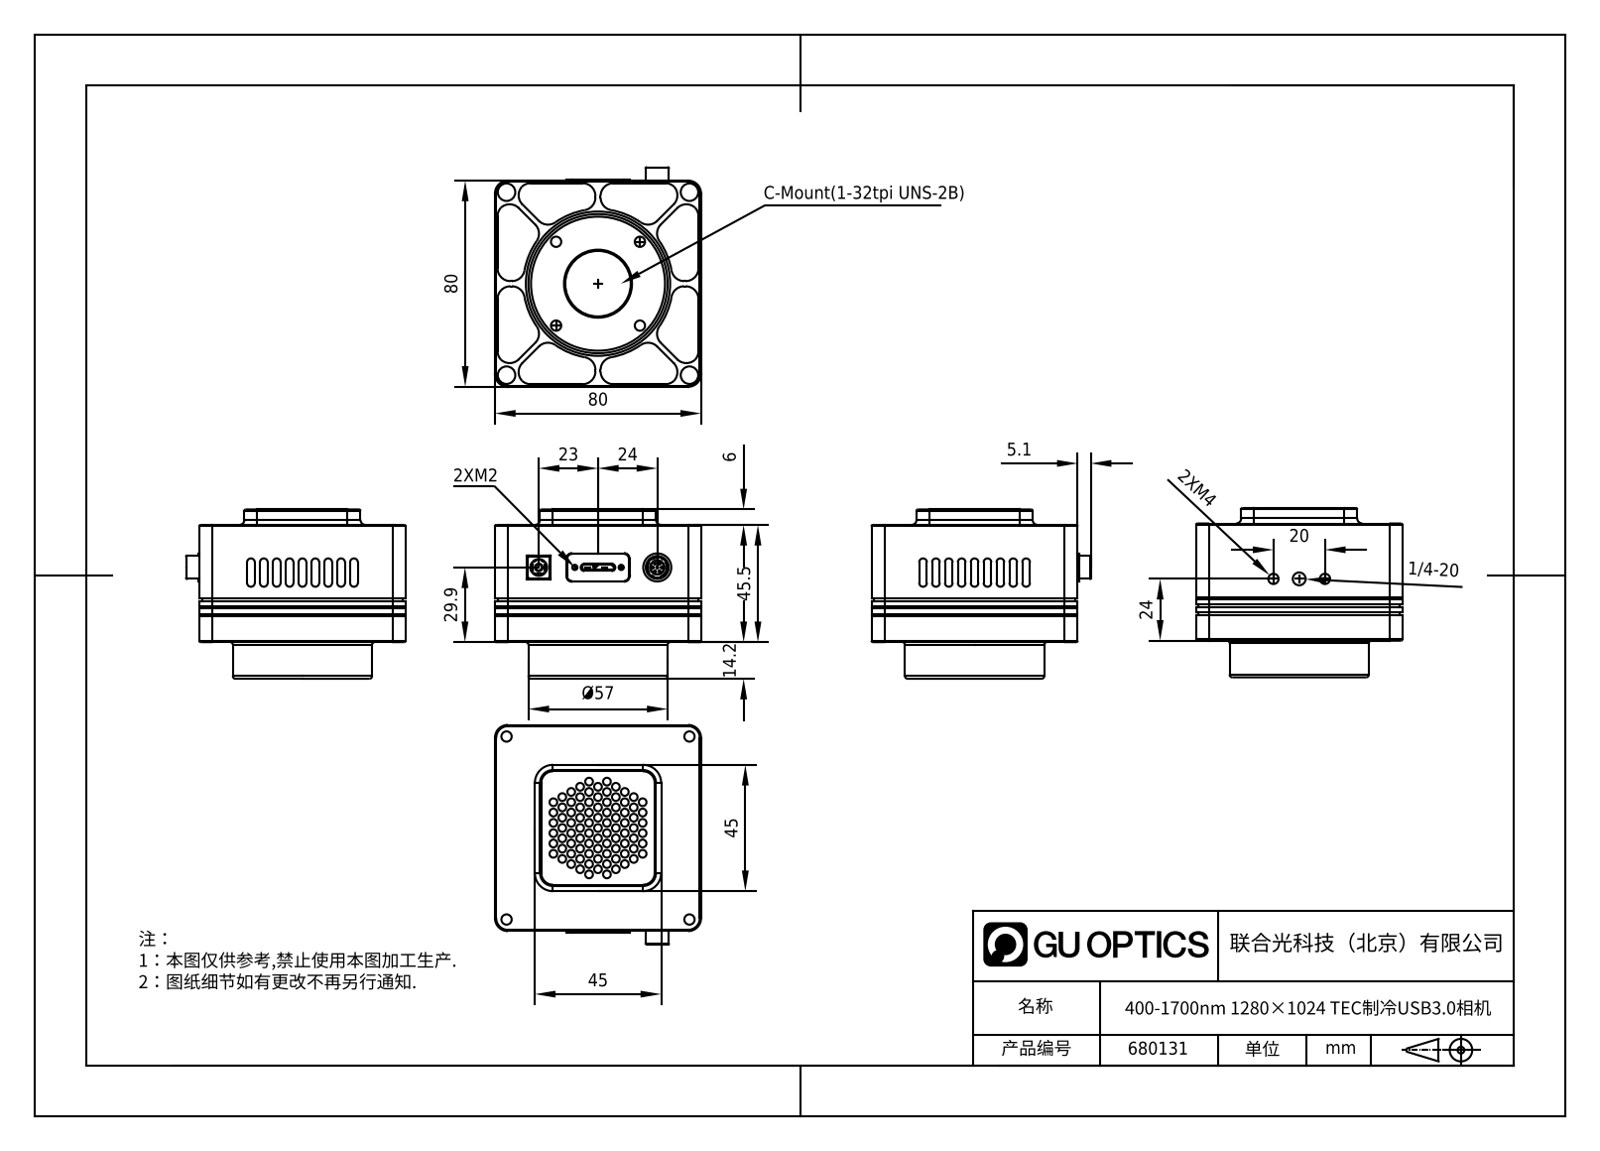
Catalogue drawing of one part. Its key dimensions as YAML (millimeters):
part_name: "680131"
step_written_by: "SolidWorks 2020 (CONFIG_CONTROL_DESIGN)"
units: millimeters
bodies: {solids: 16, faces: 1533, planar: 907, cylindrical: 526, other: 100}
overall_size: [85.1, 80, 65.7]
volume: 314597
surface_area: 44583
round_holes:
  - {diameter: 3, count: 89}
  - {diameter: 4, count: 10}
  - {diameter: 0.8, count: 7}
  - {diameter: 6.8, count: 4}
  - {diameter: 1.6, count: 2}
  - {diameter: 2.85, count: 1}
  - {diameter: 5, count: 1}
  - {diameter: 5.8, count: 1}
  - {diameter: 25.4, count: 1}
round_bosses_or_shafts:
  - {diameter: 1.2, count: 9}
  - {diameter: 0.5, count: 7}
  - {diameter: 3.6, count: 2}
  - {diameter: 54, count: 1}
  - {diameter: 10.9, count: 1}
  - {diameter: 8.9, count: 1}
  - {diameter: 7.9, count: 1}
  - {diameter: 5.6, count: 1}
partial_cylinders:
  - {radius: 5, count: 48}
  - {radius: 0.2, count: 47}
  - {radius: 0.5, count: 41}
  - {radius: 0.15, count: 39}
  - {radius: 1.5, count: 18}
  - {radius: 2, count: 16}
  - {radius: 0.25, count: 12}
  - {radius: 0.1, count: 6}
face_to_face_distances: [80, 1, 42.5, 10, 3, 6, 5, 17.2, 59.7, 79]
hole_center_spacings: [6.93, 10.58, 4, 8, 4.01, 18.33, 1.75, 12]
